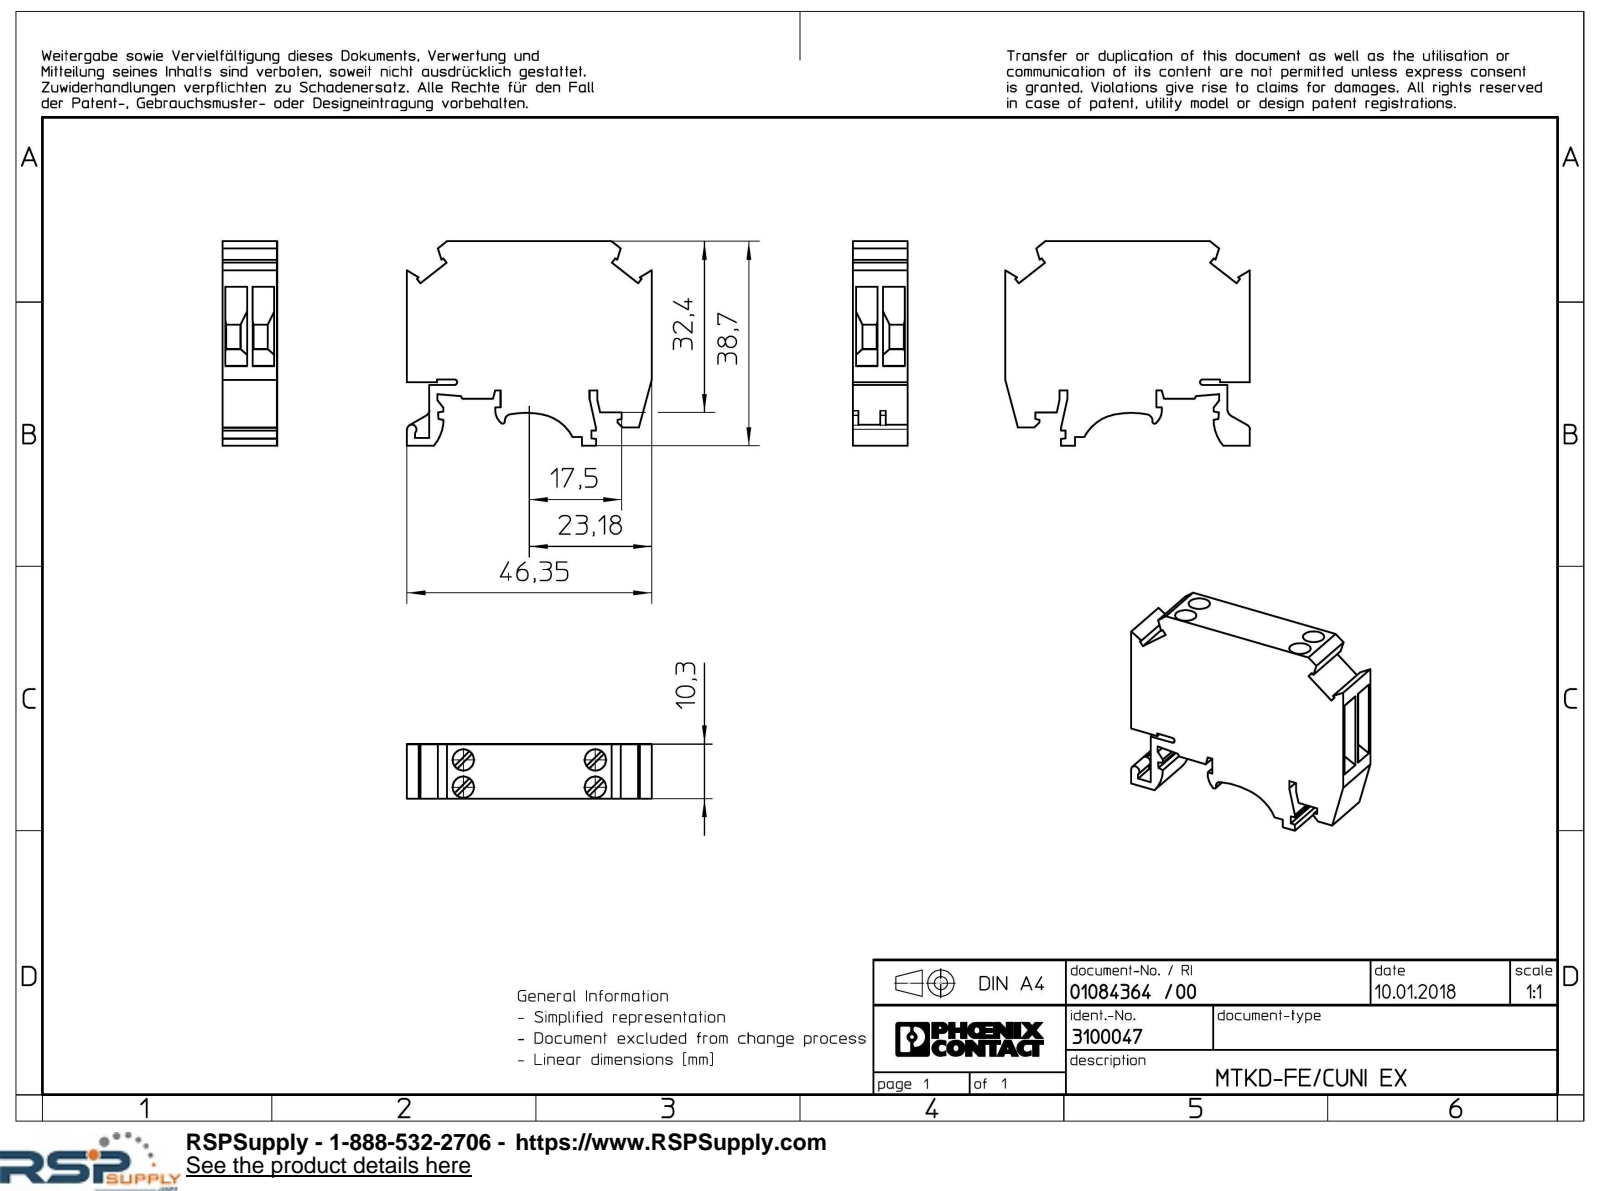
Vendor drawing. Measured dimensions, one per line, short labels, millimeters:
name: MTKD...-select
written by: Creo Elements/Direct Modeling 20.1A 29-Sep-2018 (C) Parametric Technology GmbH (AUTOMOTIVE_DESIGN)
unit: mm
bodies: 1 solid, 152 faces (134 planar, 18 cylindrical, 0 other)
size: 46.35 × 38.7 × 10.3
volume: 12 907 mm³; area: 6 723 mm²
holes: 4× ⌀4.05
rounds: 1× R0.4, 1× R0.53, 1× R0.9, 1× R1, 1× R1.2, 1× R3.35, 1× R7.47, 1× R8
face distances: 10.3, 5.15, 4.1, 1.23, 3.93, 2.7, 2.87, 1.05, 4.62, 0.53
hole spacings: 5.15, 25, 25.52
